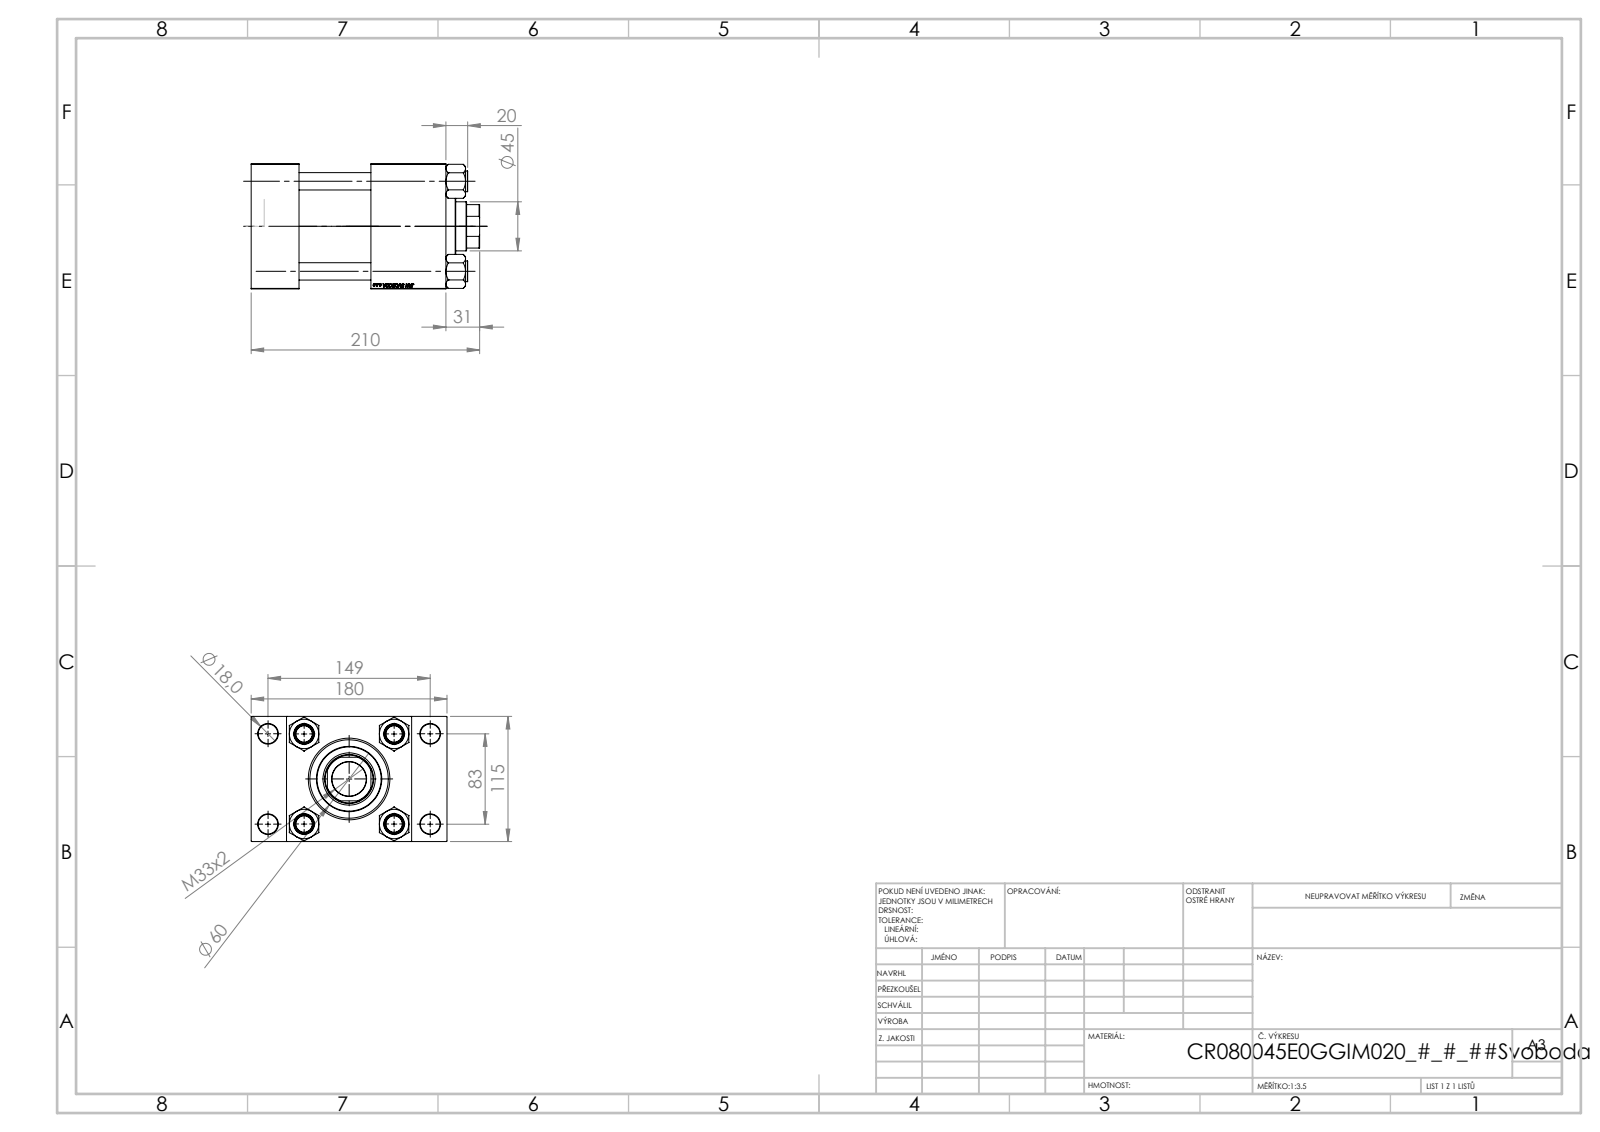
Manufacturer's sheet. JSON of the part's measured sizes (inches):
{"part_name": "V215_VC_A; V215CR_VCP_E; V215CR_E_Body; NUT_M5_E (+1 more)", "step_written_by": "SolidWorks 2019 (CONFIG_CONTROL_DESIGN)", "units": "inches", "bodies": {"solids": 11, "faces": 1185, "planar": 546, "cylindrical": 87, "other": 552}, "overall_size": [8.268, 7.087, 4.528], "volume_in3": 129.3, "surface_area_in2": 488.2, "round_holes": [[0.63, 4], [0.709, 4], [0.276, 2], [1.041, 2], [1.378, 2], [1.24, 1], [1.772, 1], [1.89, 1], [2.402, 1], [2.835, 1], [3.15, 1]], "round_bosses_or_shafts": [[0.748, 4], [3.386, 1], [2.362, 1]], "partial_cylinders_radius": [[0.866, 1]], "face_to_face_distances": [4.528, 1.732, 7.047, 5.315, 1.28, 5.807, 4.331, 2.598, 2.717, 7.087], "hole_center_spacings": [1.305, 2.302, 3.256, 3.357, 3.513, 4.561, 5.607, 3.268]}
